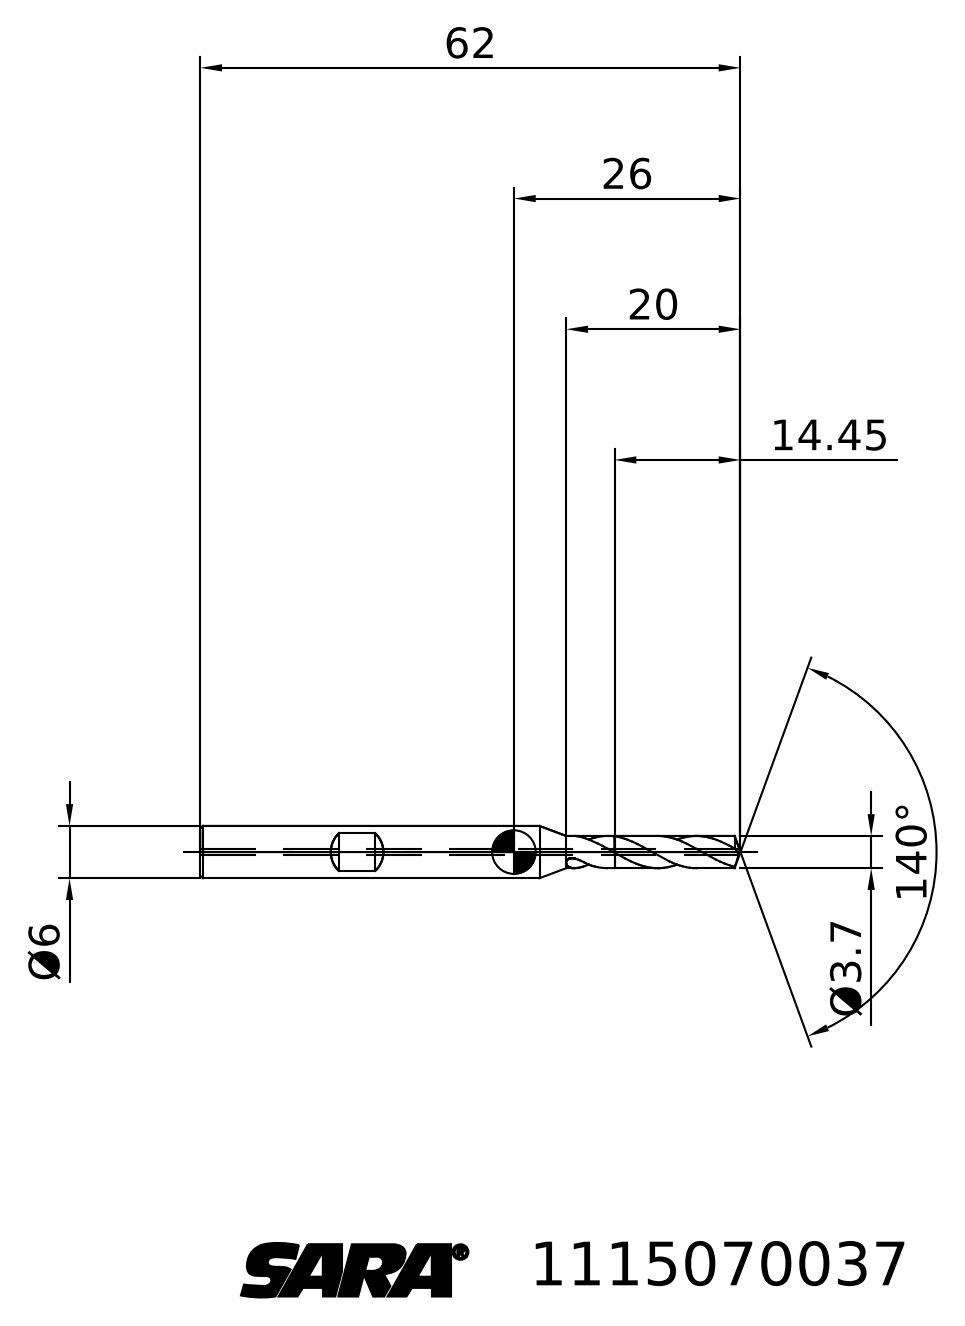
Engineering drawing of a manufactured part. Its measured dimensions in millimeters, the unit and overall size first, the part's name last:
Units: millimetres
Overall size (bounding box): 62 × 9.81 × 6
Main face-to-face distances: 47.55
Volume: 1 287 mm³ · Surface area: 1 076 mm²
Bodies: 2 solids, 30 faces (6 planar, 0 cylindrical, 24 other)
STEP written by: TDM (AUTOMOTIVE_DESIGN)
